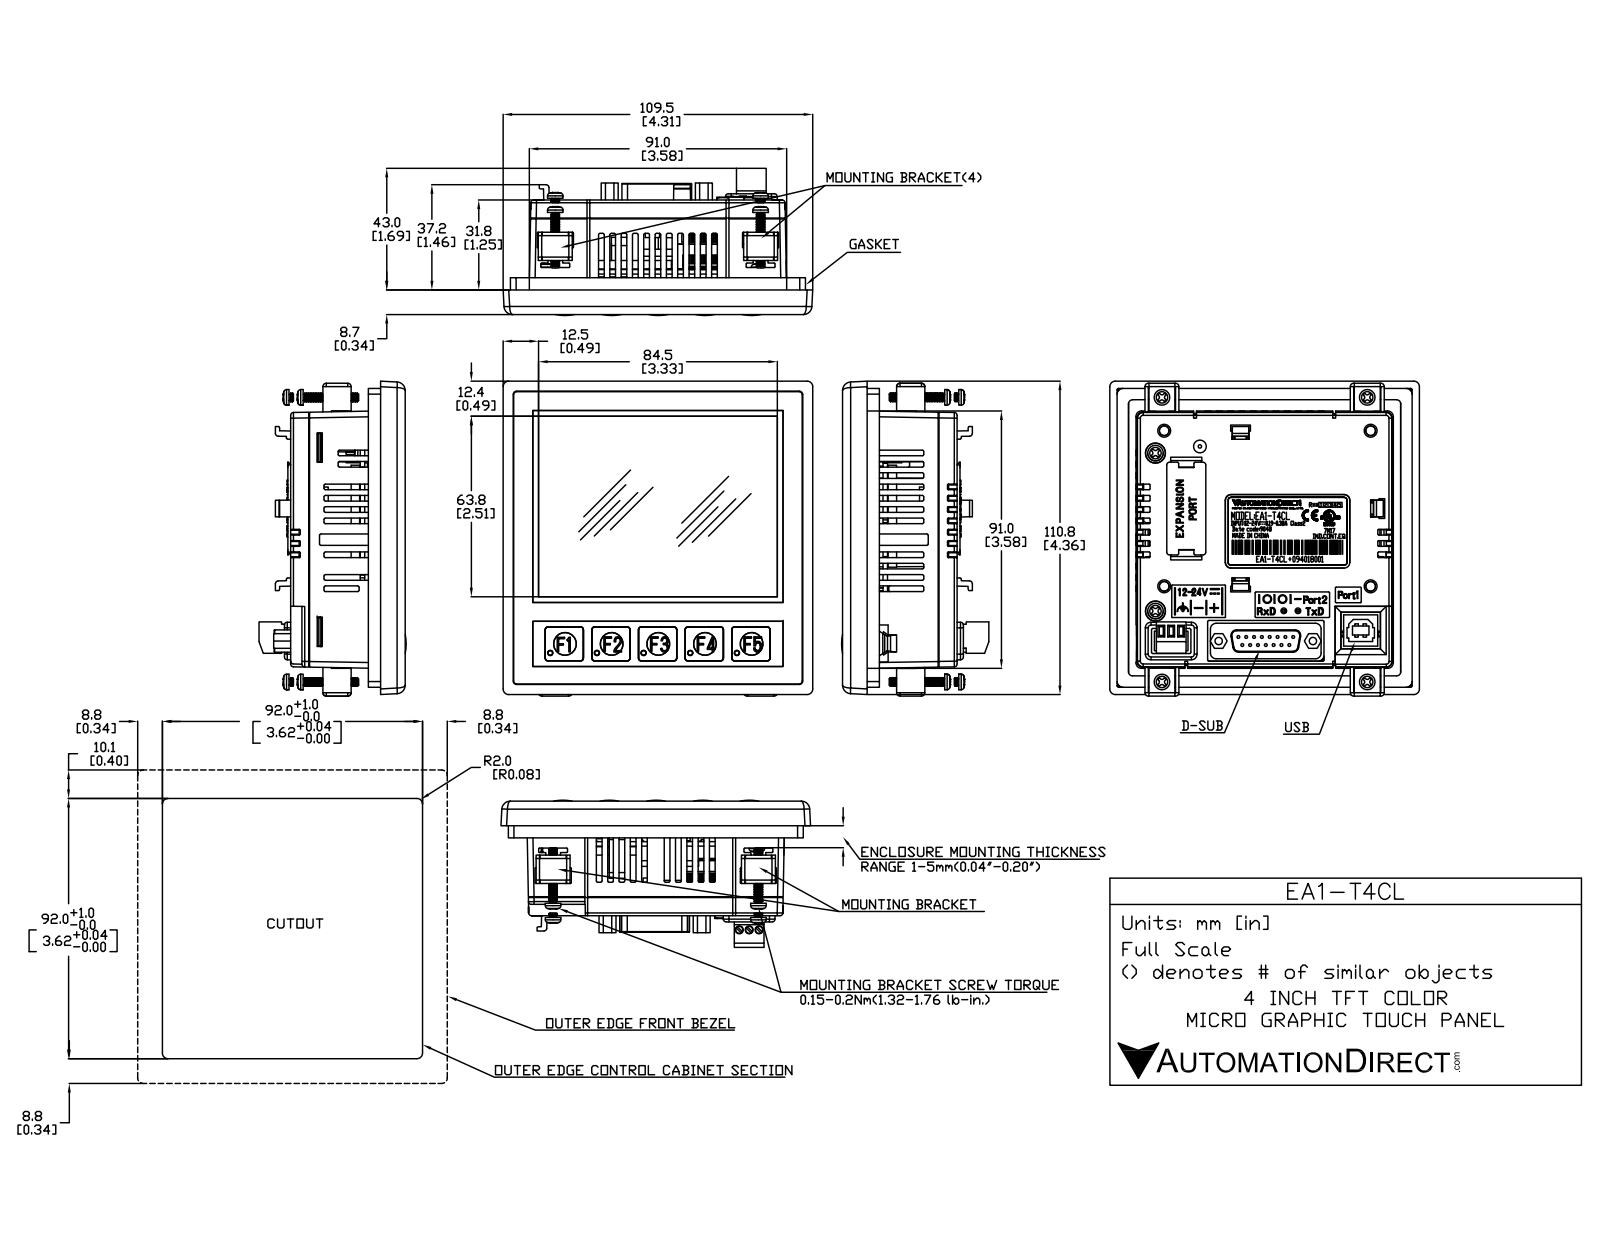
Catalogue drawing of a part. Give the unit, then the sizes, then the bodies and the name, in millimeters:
Units: millimetres
Overall size (bounding box): 110.8 × 109.5 × 46.7
Round holes (diameter × count): ⌀2 ×5, ⌀8.5 ×5, ⌀3.5 ×4
Round bosses / shafts (diameter × count): ⌀7.5 ×4
Partial cylindrical surfaces — rounded edges, fillets, slot ends (radius × count): R1 ×44, R2 ×20, R2.5 ×4, R3 ×4
Main face-to-face distances: 2, 2.9, 89, 5.9, 30.1, 33, 3, 27.1, 32.1, 35
Hole centre spacings: 16.5, 33, 5.62, 12.13, 21.46, 49.5, 28.41, 37.87
Volume: 92 811 mm³ · Surface area: 88 211 mm²
Bodies: 22 solids, 466 faces (287 planar, 153 cylindrical, 26 other)
Part name (STEP PRODUCT): EA1-T4CL
STEP written by: SolidWorks 2009 (AUTOMOTIVE_DESIGN)
